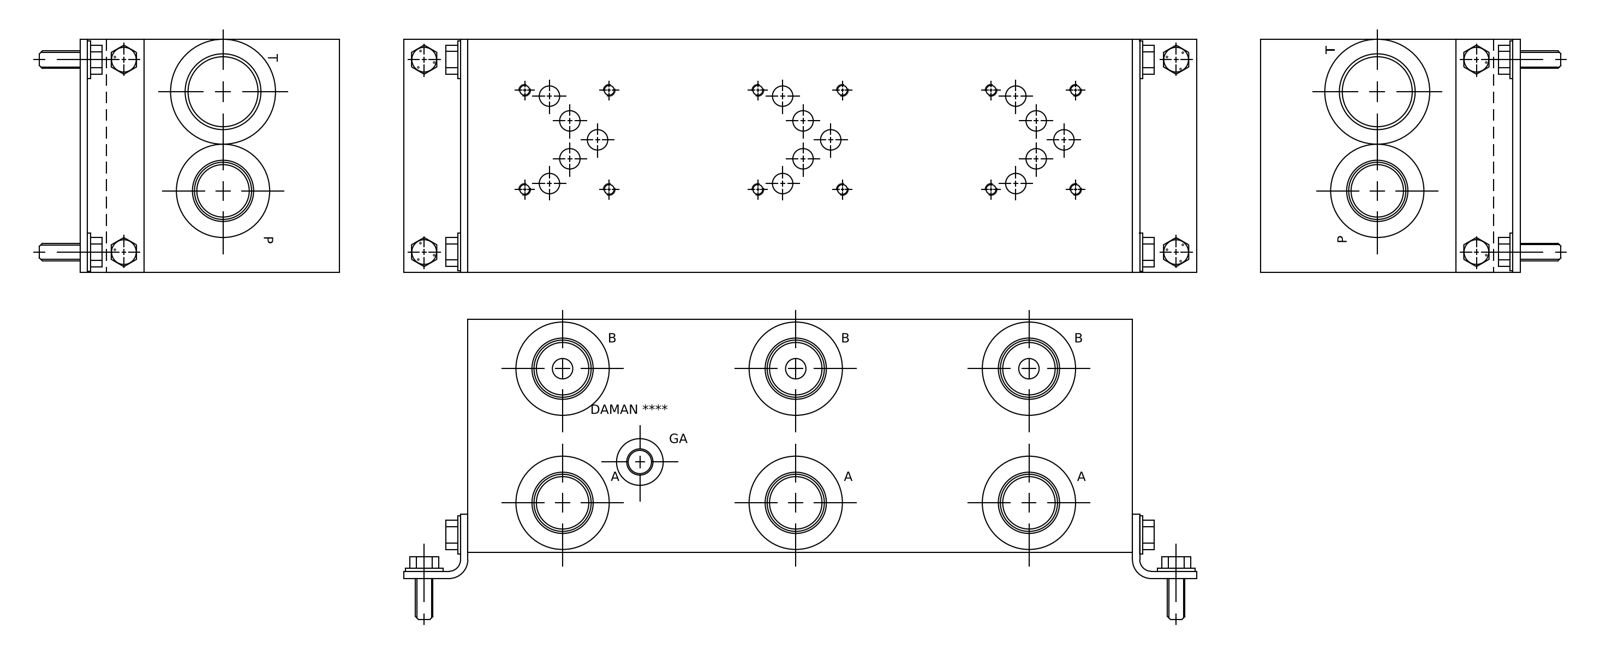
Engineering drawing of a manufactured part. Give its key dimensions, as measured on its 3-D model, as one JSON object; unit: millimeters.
{"part_name": "Part_AD05JP035S_3D", "step_written_by": "Autodesk Inventor 2020 (AUTOMOTIVE_DESIGN)", "units": "millimeters", "bodies": {"solids": 1, "faces": 773, "planar": 395, "cylindrical": 107, "other": 271}, "overall_size": [361.95, 127, 127], "volume_mm3": 5476000, "surface_area_mm2": 265690, "round_holes": [[5.11, 12], [6.35, 12], [31.27, 7], [33.76, 7], [49.12, 7], [10.31, 6], [11.13, 6], [28.57, 6], [9.53, 5], [33.35, 5], [35.51, 5], [33.34, 3]], "face_to_face_distances": [127, 361.95, 0.79, 126.21, 361.16, 360.37, 19.05, 19.84, 107.16, 342.11], "hole_center_spacings": [127, 137.99, 254, 13.88, 46.05, 53.97, 32.69, 52.57]}
